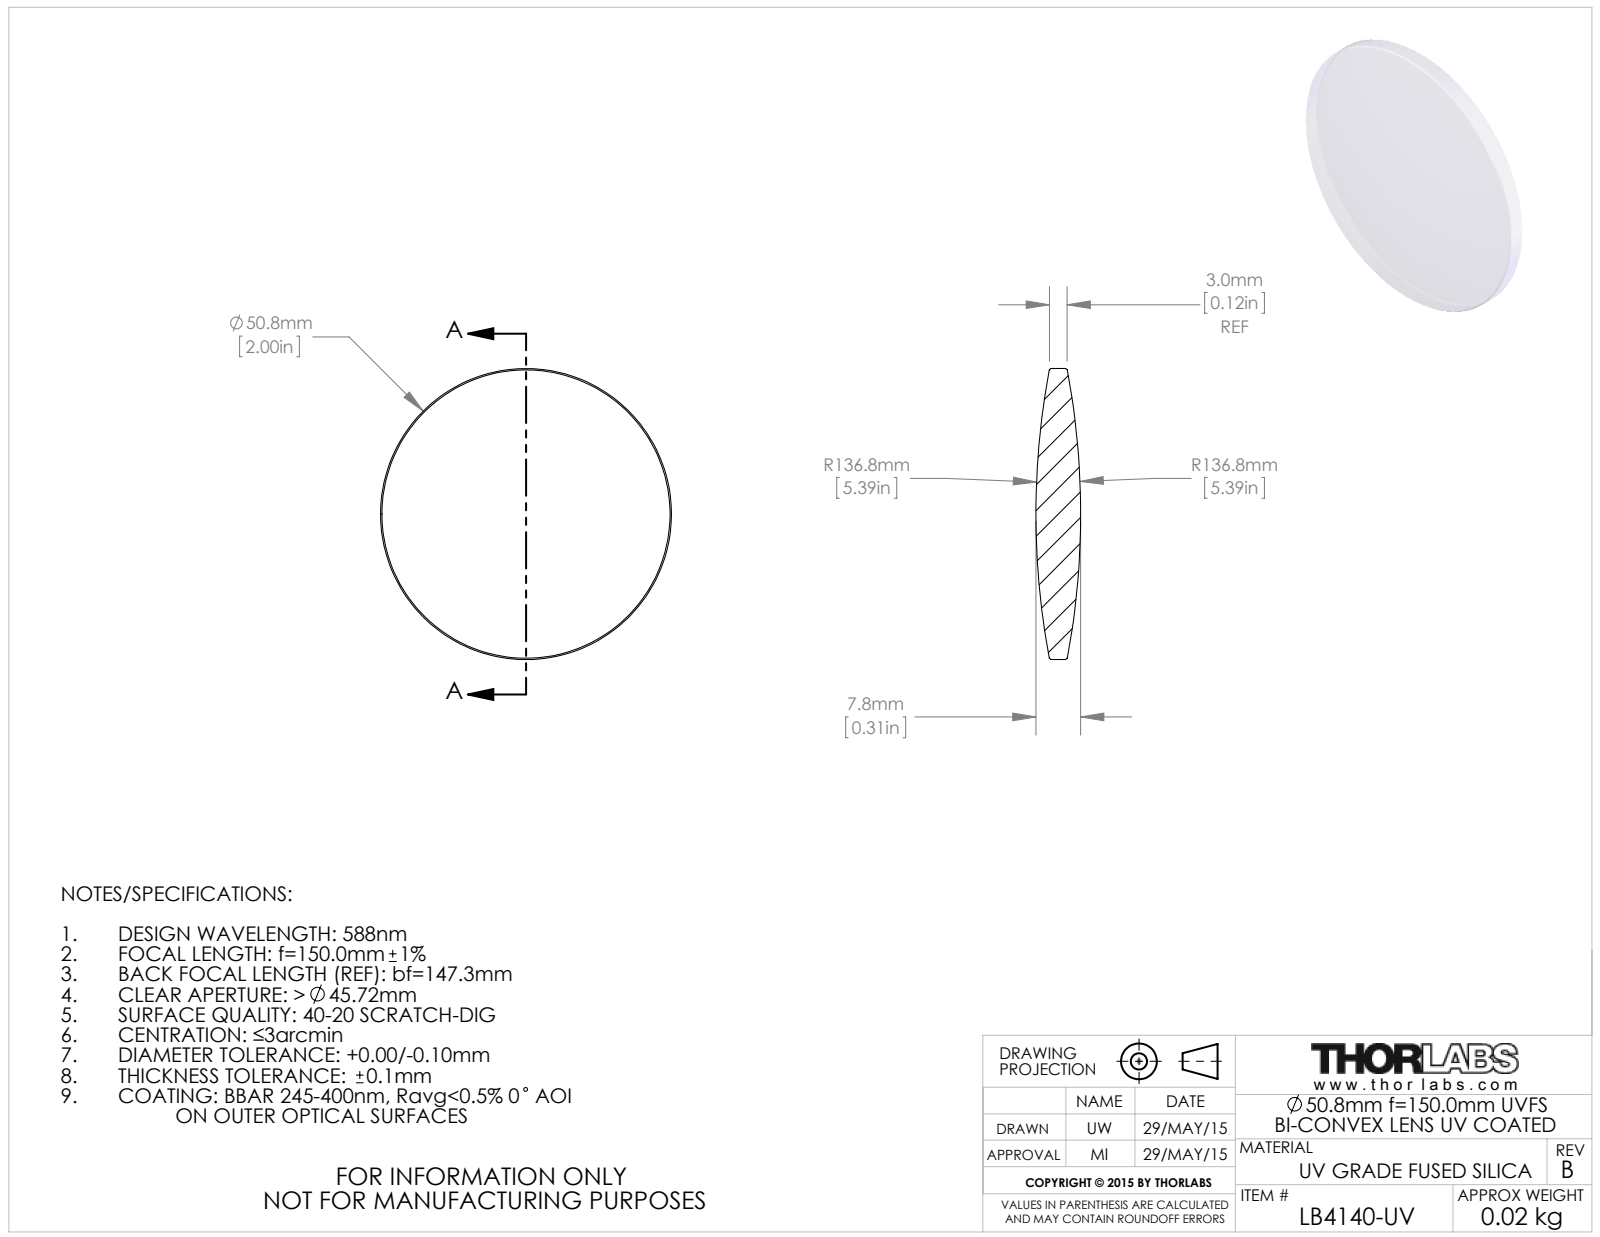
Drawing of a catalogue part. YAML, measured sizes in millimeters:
part_name: "4334-E0W"
step_written_by: "SolidWorks 2014 (CONFIG_CONTROL_DESIGN)"
units: millimeters
bodies: {solids: 1, faces: 10, planar: 0, cylindrical: 2, other: 8}
overall_size: [50.8, 50.8, 7.8]
volume: 10992
surface_area: 4538
round_bosses_or_shafts:
  - {diameter: 50.8, count: 1}
